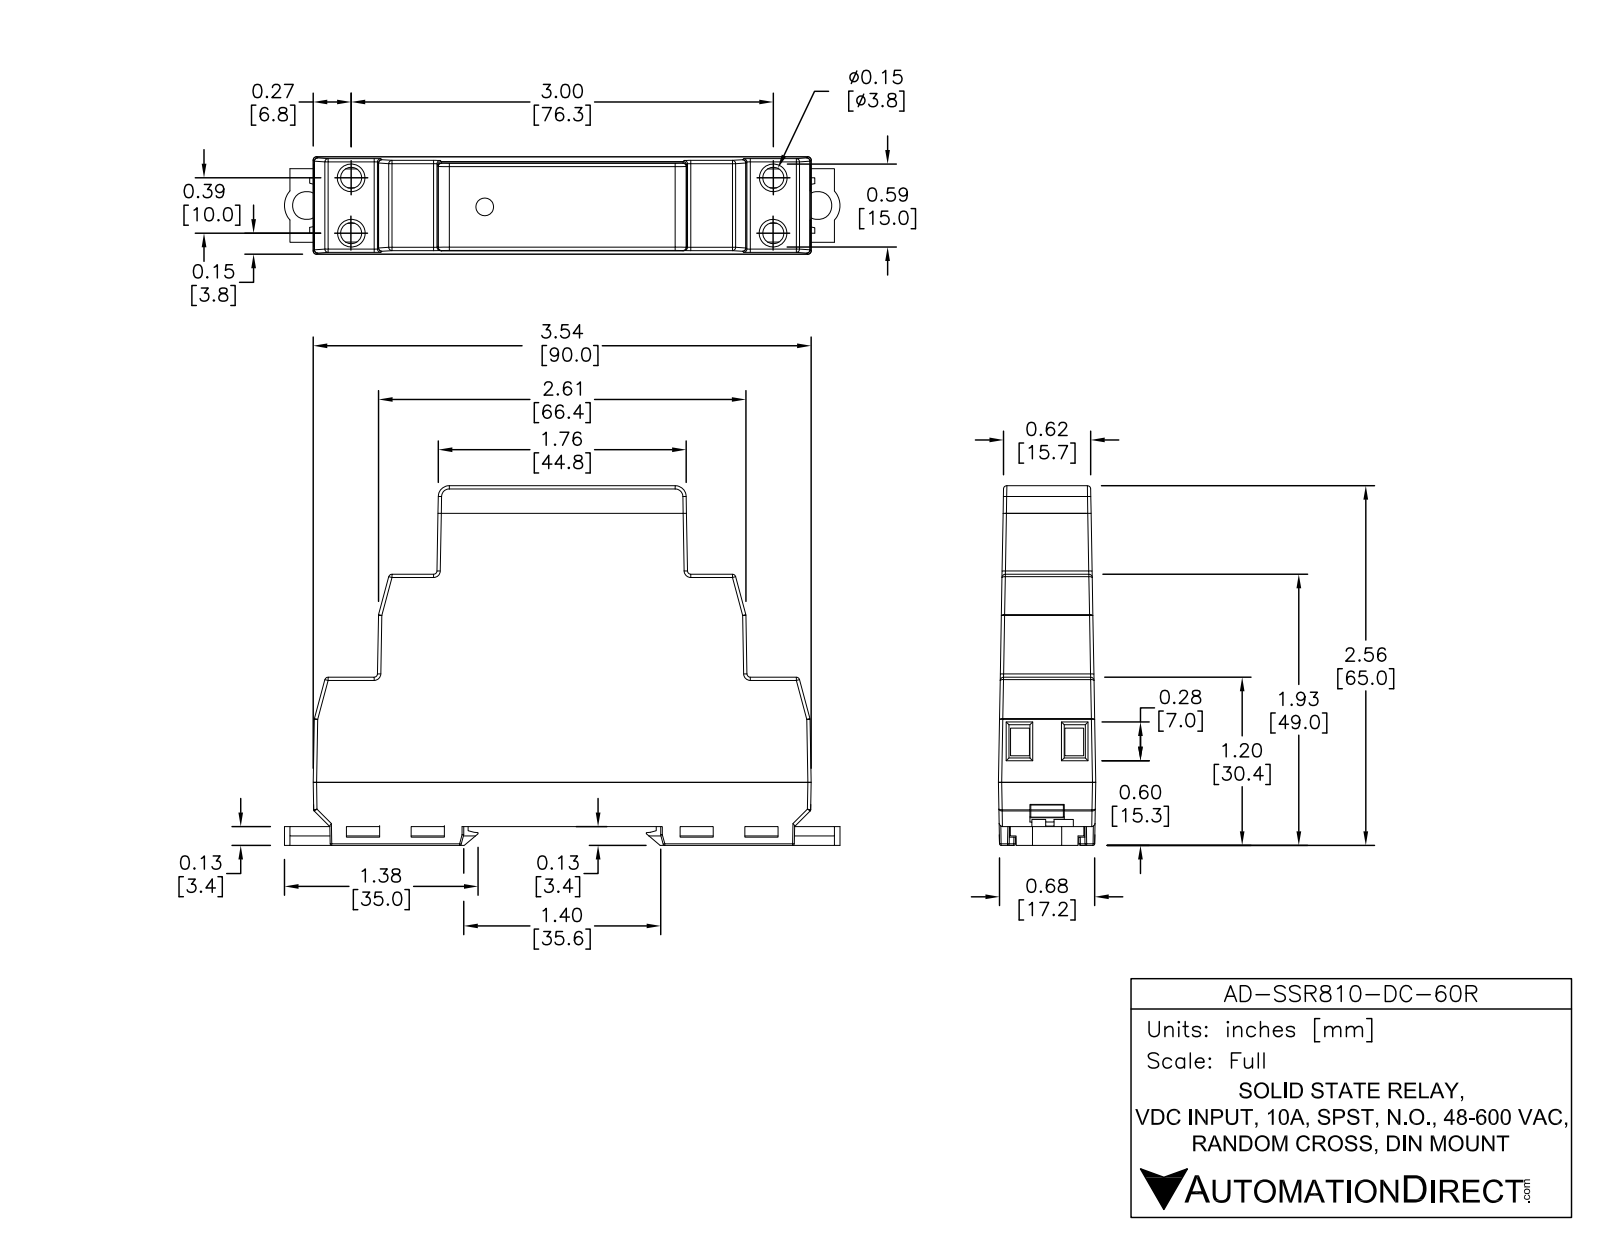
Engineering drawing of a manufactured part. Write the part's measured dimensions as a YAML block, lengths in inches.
part_name: "AD-SSR810-DC-60R"
step_written_by: "SolidWorks 2013 (AUTOMOTIVE_DESIGN)"
units: inches
bodies: {solids: 1, faces: 841, planar: 487, cylindrical: 78, other: 276}
overall_size: [3.924, 2.616, 0.685]
volume: 4.605
surface_area: 24.23
round_holes:
  - {diameter: 0.19, count: 4}
  - {diameter: 0.2, count: 2}
round_bosses_or_shafts:
  - {diameter: 0.105, count: 1}
partial_cylinders:
  - {radius: 0.015, count: 41}
  - {radius: 0.06, count: 2}
  - {radius: 0.172, count: 2}
face_to_face_distances: [2.525, 0.049, 2.574, 0.425, 2.215, 0.025, 0.05, 1.934, 1.885, 0.64]
hole_center_spacings: [0.338, 3.3, 0.364, 3.01, 3.032, 3.58]
